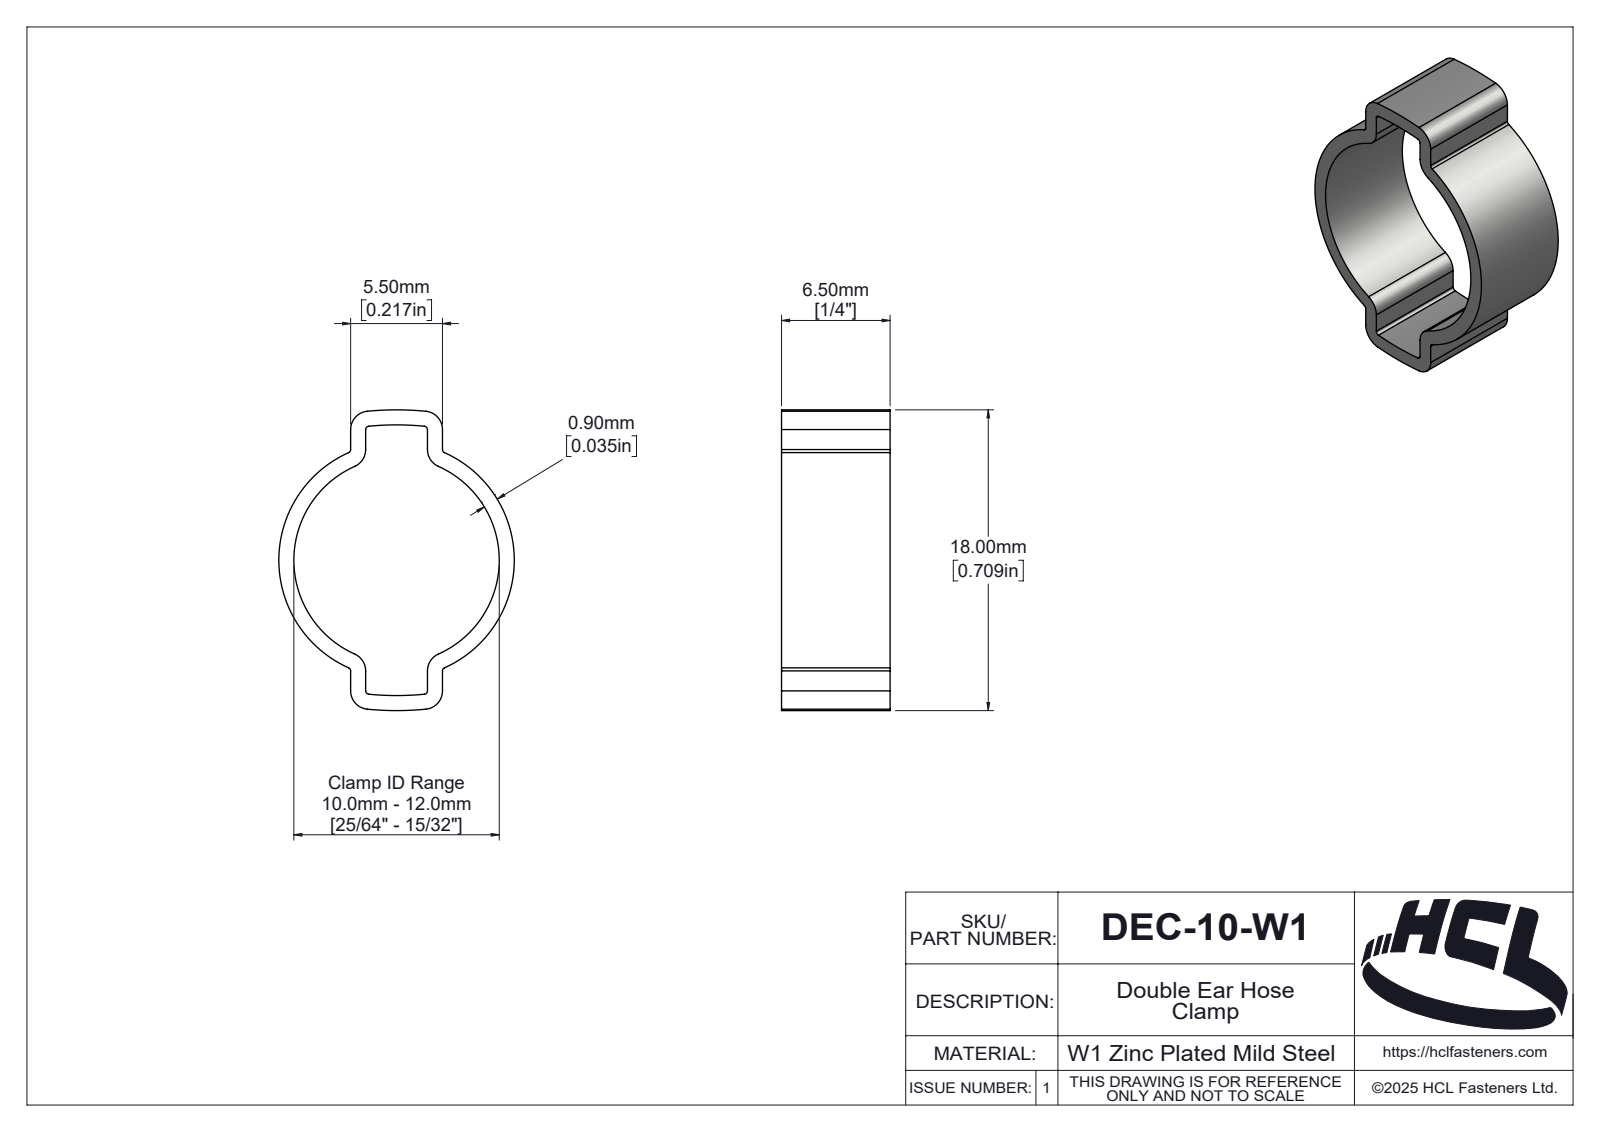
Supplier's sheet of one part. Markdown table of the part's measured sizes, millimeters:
| quantity | value |
| --- | --- |
| part name | DEC-10-W1 |
| STEP written by | SolidWorks 2025 (AUTOMOTIVE_DESIGN) |
| units | millimeters |
| bodies | 1 solid, 137 faces (12 planar, 76 cylindrical, 49 other) |
| overall size | 18 × 14.1 × 6.5 |
| volume | 286 mm³ |
| surface area | 726 mm² |
| partial cylindrical surfaces (radius × count) | 0.2 × 8, 1.1 × 8, 17.16 × 2, 18.06 × 2, 0.13 × 1, 0.54 × 1, 0.67 × 1, 0.71 × 1 |
| main face-to-face distances | 6.5, 0.9, 4.6, 5.5, 3.7, 2.57, 1.67, 2.03, 2.93, 2.67 |
